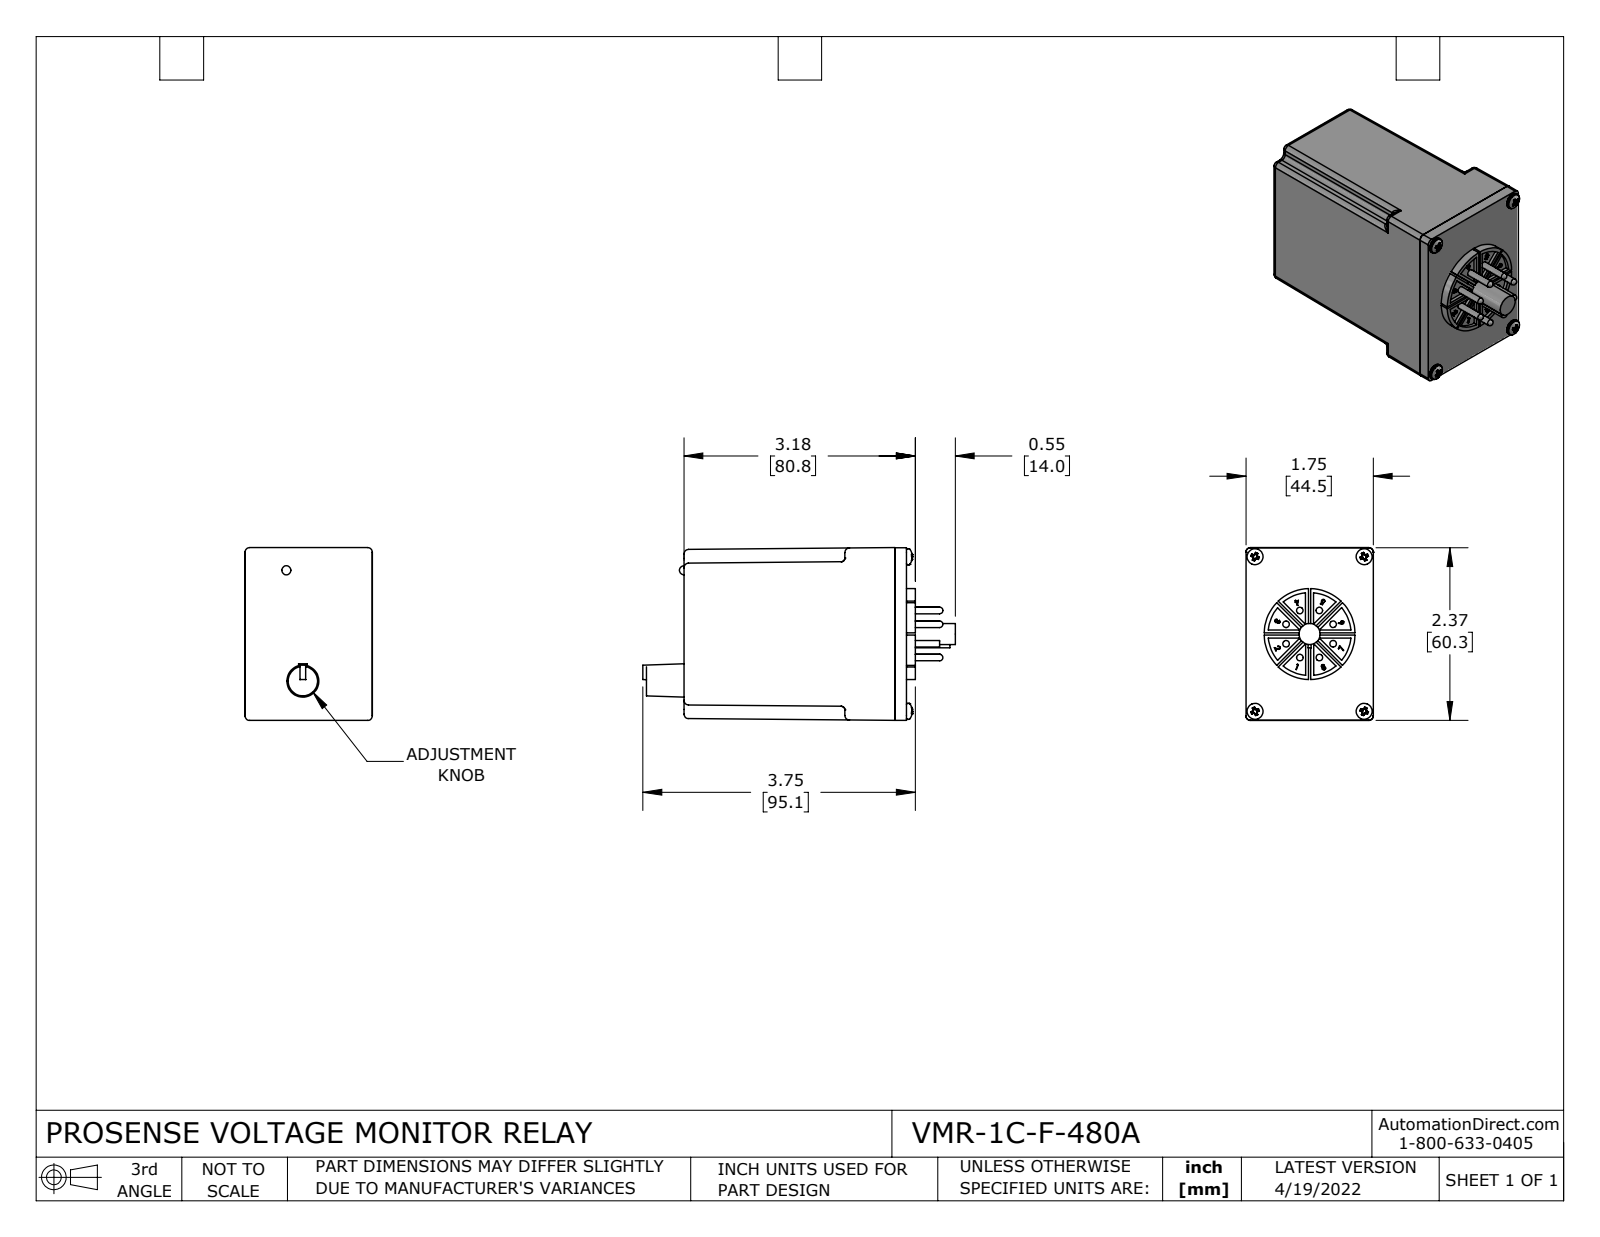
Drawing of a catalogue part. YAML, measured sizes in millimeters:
part_name: "VMR-1C-F-480A"
step_written_by: "SolidWorks 2021 (CONFIG_CONTROL_DESIGN)"
units: millimeters
bodies: {solids: 17, faces: 542, planar: 221, cylindrical: 164, other: 157}
overall_size: [109.1, 60.3, 44.5]
volume: 202100
surface_area: 29540
round_holes:
  - {diameter: 3.2, count: 4}
round_bosses_or_shafts:
  - {diameter: 2.3, count: 8}
  - {diameter: 5.6, count: 4}
  - {diameter: 31.8, count: 1}
  - {diameter: 7.4, count: 1}
partial_cylinders:
  - {radius: 1.6, count: 32}
  - {radius: 0.1, count: 8}
  - {radius: 1.3, count: 4}
  - {radius: 14.5, count: 1}
face_to_face_distances: [73.7, 4.1, 77.7, 1.8, 5.8, 79.5, 4.8, 1.3, 3, 7.1]
hole_center_spacings: [38.1, 54, 66.1]
